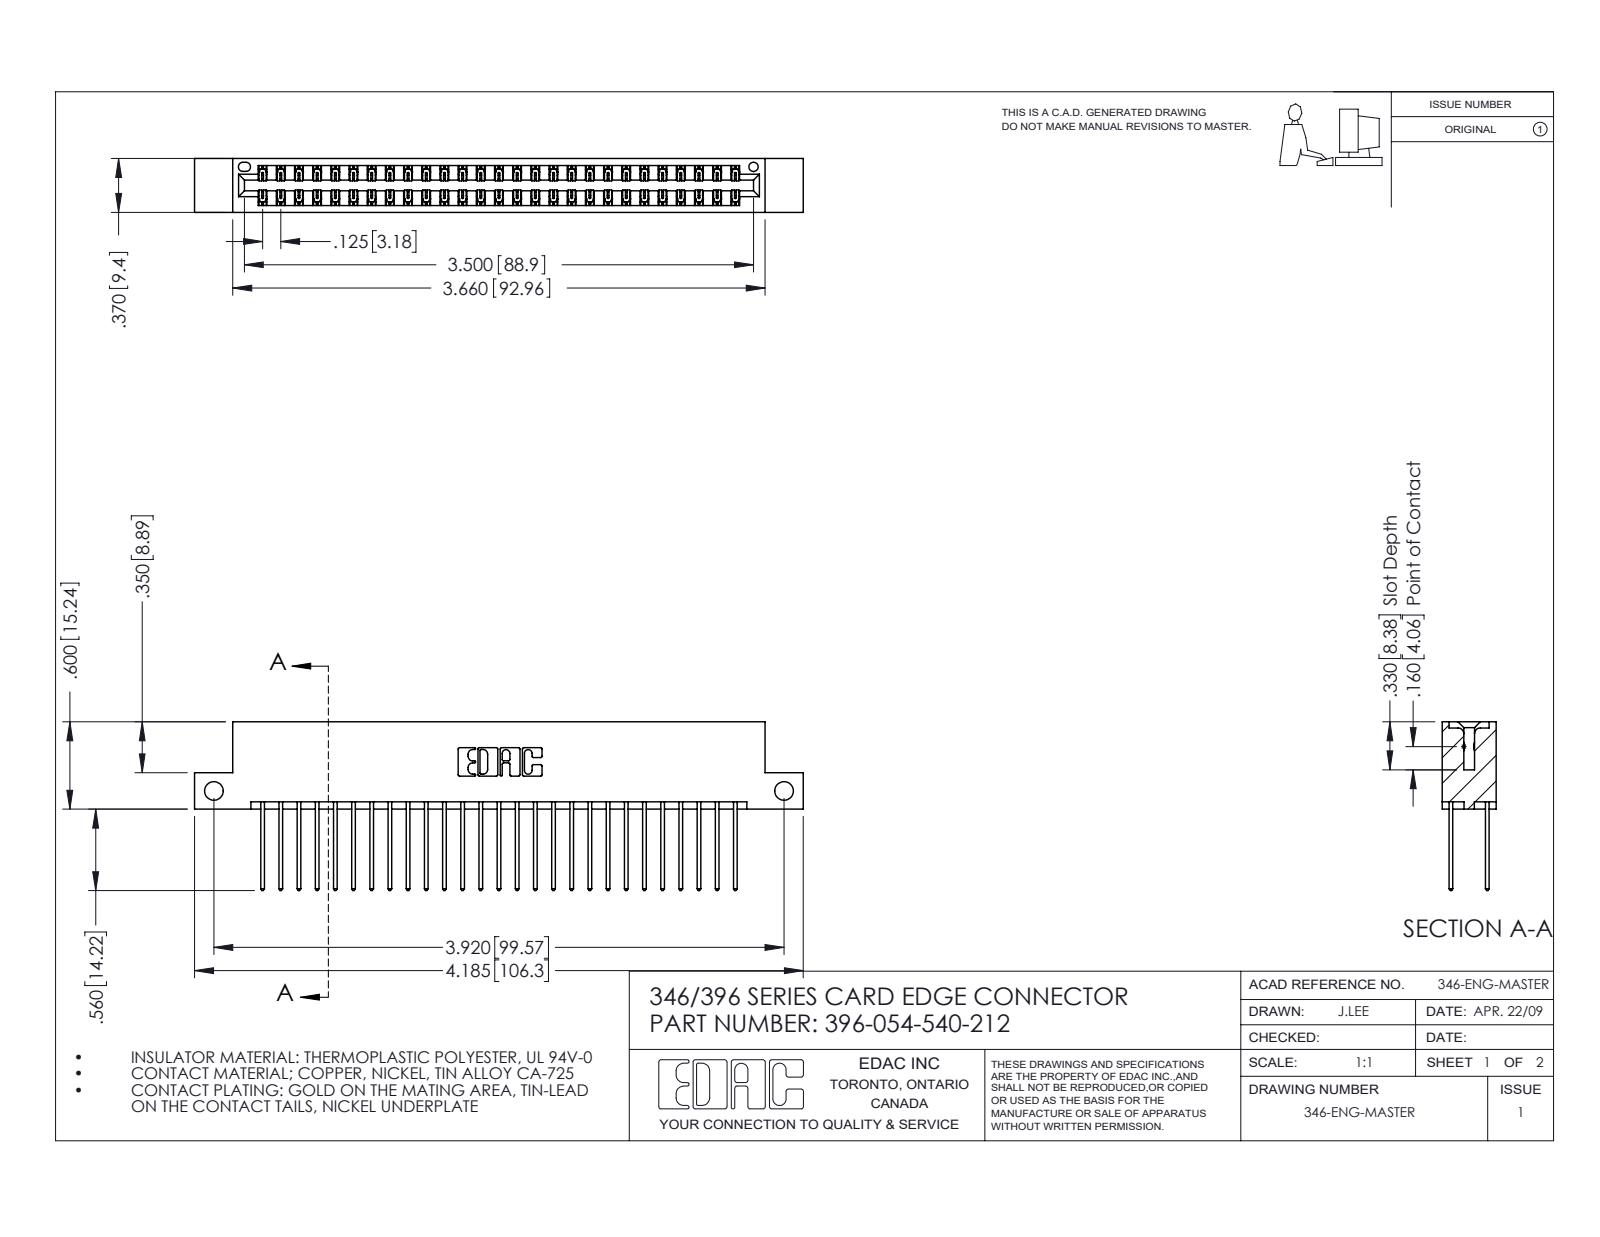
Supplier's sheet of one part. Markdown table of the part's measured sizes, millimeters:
| quantity | value |
| --- | --- |
| part name | 345-292-001_345-293-140; 346 Part_Flush Mounting Lugs - Side Mount; 396-054-540-212 |
| STEP written by | SolidWorks 2016 (CONFIG_CONTROL_DESIGN) |
| units | millimeters |
| bodies | 55 solids, 2930 faces (1966 planar, 964 cylindrical, 0 other) |
| overall size | 106.3 × 29.5 × 9.4 |
| volume | 10 400 mm³ |
| surface area | 14 850 mm² |
| round holes (diameter × count) | 3.3 × 2, 1.6 × 1 |
| partial cylindrical surfaces (radius × count) | 0.2 × 81, 0.3 × 54, 0.3 × 22, 0.2 × 6, 0.8 × 6, 0.7 × 3, 0.4 × 2, 0.6 × 2 |
| main face-to-face distances | 1.2, 8.2, 6.4, 1.8, 7.6, 0.6, 9.4, 7, 3.8, 5.6 |
| hole center spacings | 99.6 |
